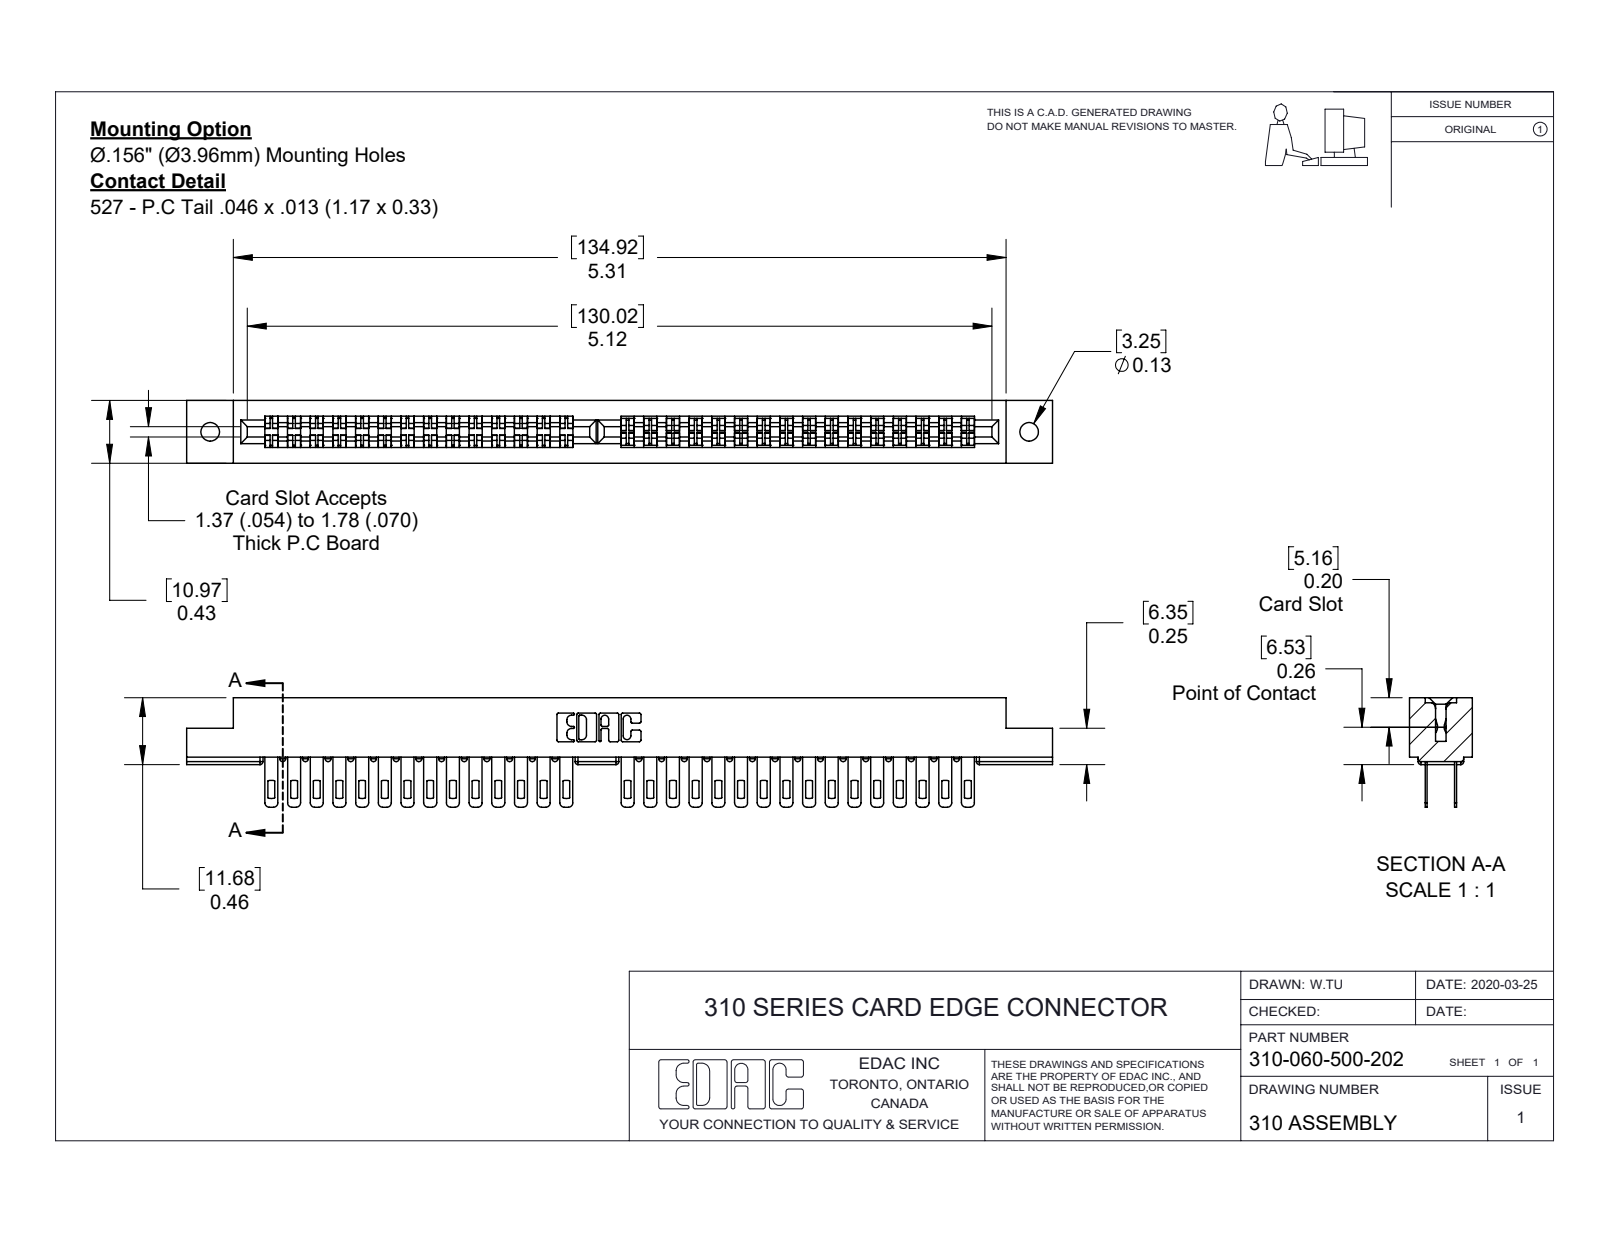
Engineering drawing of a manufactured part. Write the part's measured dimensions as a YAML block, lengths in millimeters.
part_name: "310-060-500-202; 307-290-001_500; 310 Part_.128 Dia. Hole"
step_written_by: "SolidWorks 2016 (CONFIG_CONTROL_DESIGN)"
units: millimeters
bodies: {solids: 61, faces: 2926, planar: 1884, cylindrical: 978, other: 64}
overall_size: [151.21, 19.13, 10.97]
volume: 13146
surface_area: 18626
round_holes:
  - {diameter: 3.25, count: 2}
partial_cylinders:
  - {radius: 0.51, count: 98}
  - {radius: 0.76, count: 60}
  - {radius: 1.59, count: 30}
  - {radius: 0.25, count: 22}
  - {radius: 0.17, count: 6}
  - {radius: 0.8, count: 6}
  - {radius: 0.3, count: 4}
  - {radius: 0.64, count: 4}
face_to_face_distances: [2.76, 8.22, 0.33, 0.38, 4.75, 10.98, 3.14, 7.84, 5.08, 5.46]
hole_center_spacings: [143]
